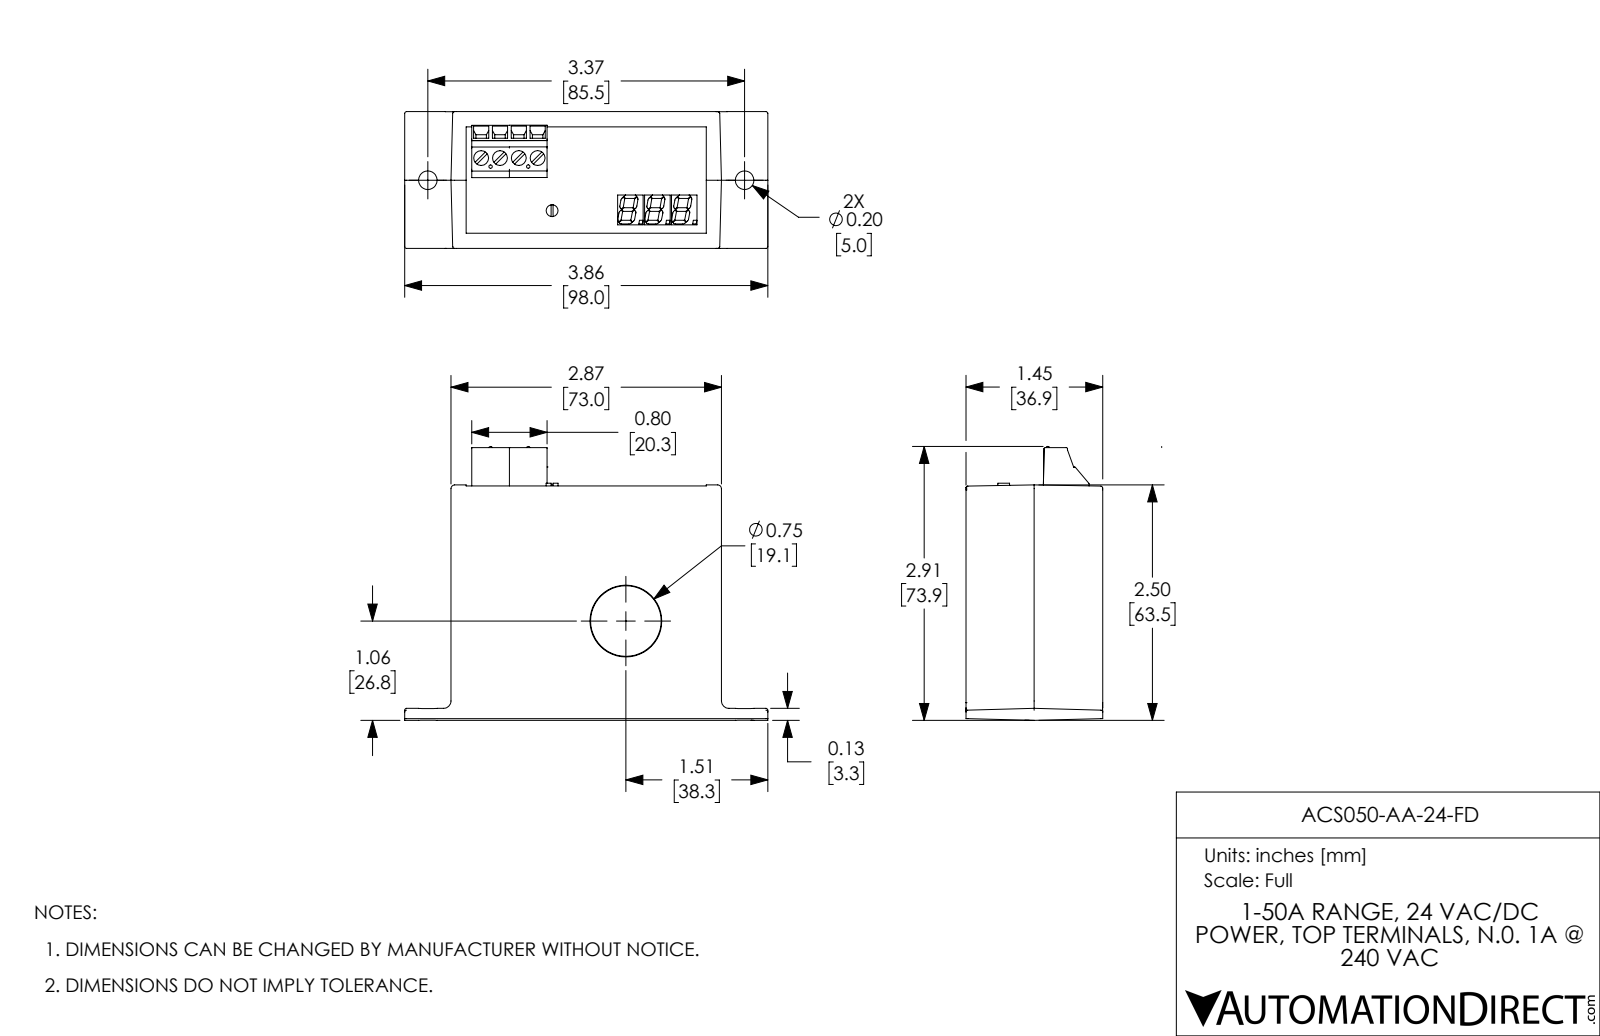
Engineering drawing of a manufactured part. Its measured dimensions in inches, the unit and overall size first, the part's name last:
Units: inches
Overall size (bounding box): 3.858 × 2.909 × 1.453
Round holes (diameter × count): ⌀0.059 ×4, ⌀0.157 ×4, ⌀0.197 ×2, ⌀0.75 ×1
Round bosses / shafts (diameter × count): ⌀0.126 ×1
Partial cylindrical surfaces — rounded edges, fillets, slot ends (radius × count): R0.02 ×16, R0.012 ×12, R0.039 ×4, R0.079 ×4
Main face-to-face distances: 1.453, 2.874, 0.128, 0.048, 0.161, 0.11, 1.343, 1.291, 0.051, 1.181
Hole centre spacings: 0.2, 0.4, 2.385, 3.986, 0.6, 0.614, 0.802, 0.995
Volume: 9.631 in³ · Surface area: 38.41 in²
Bodies: 1 solid, 461 faces (308 planar, 74 cylindrical, 79 other)
Part name (STEP PRODUCT): ACS050-AA-24-FD
STEP written by: SolidWorks 2017 (AUTOMOTIVE_DESIGN)
